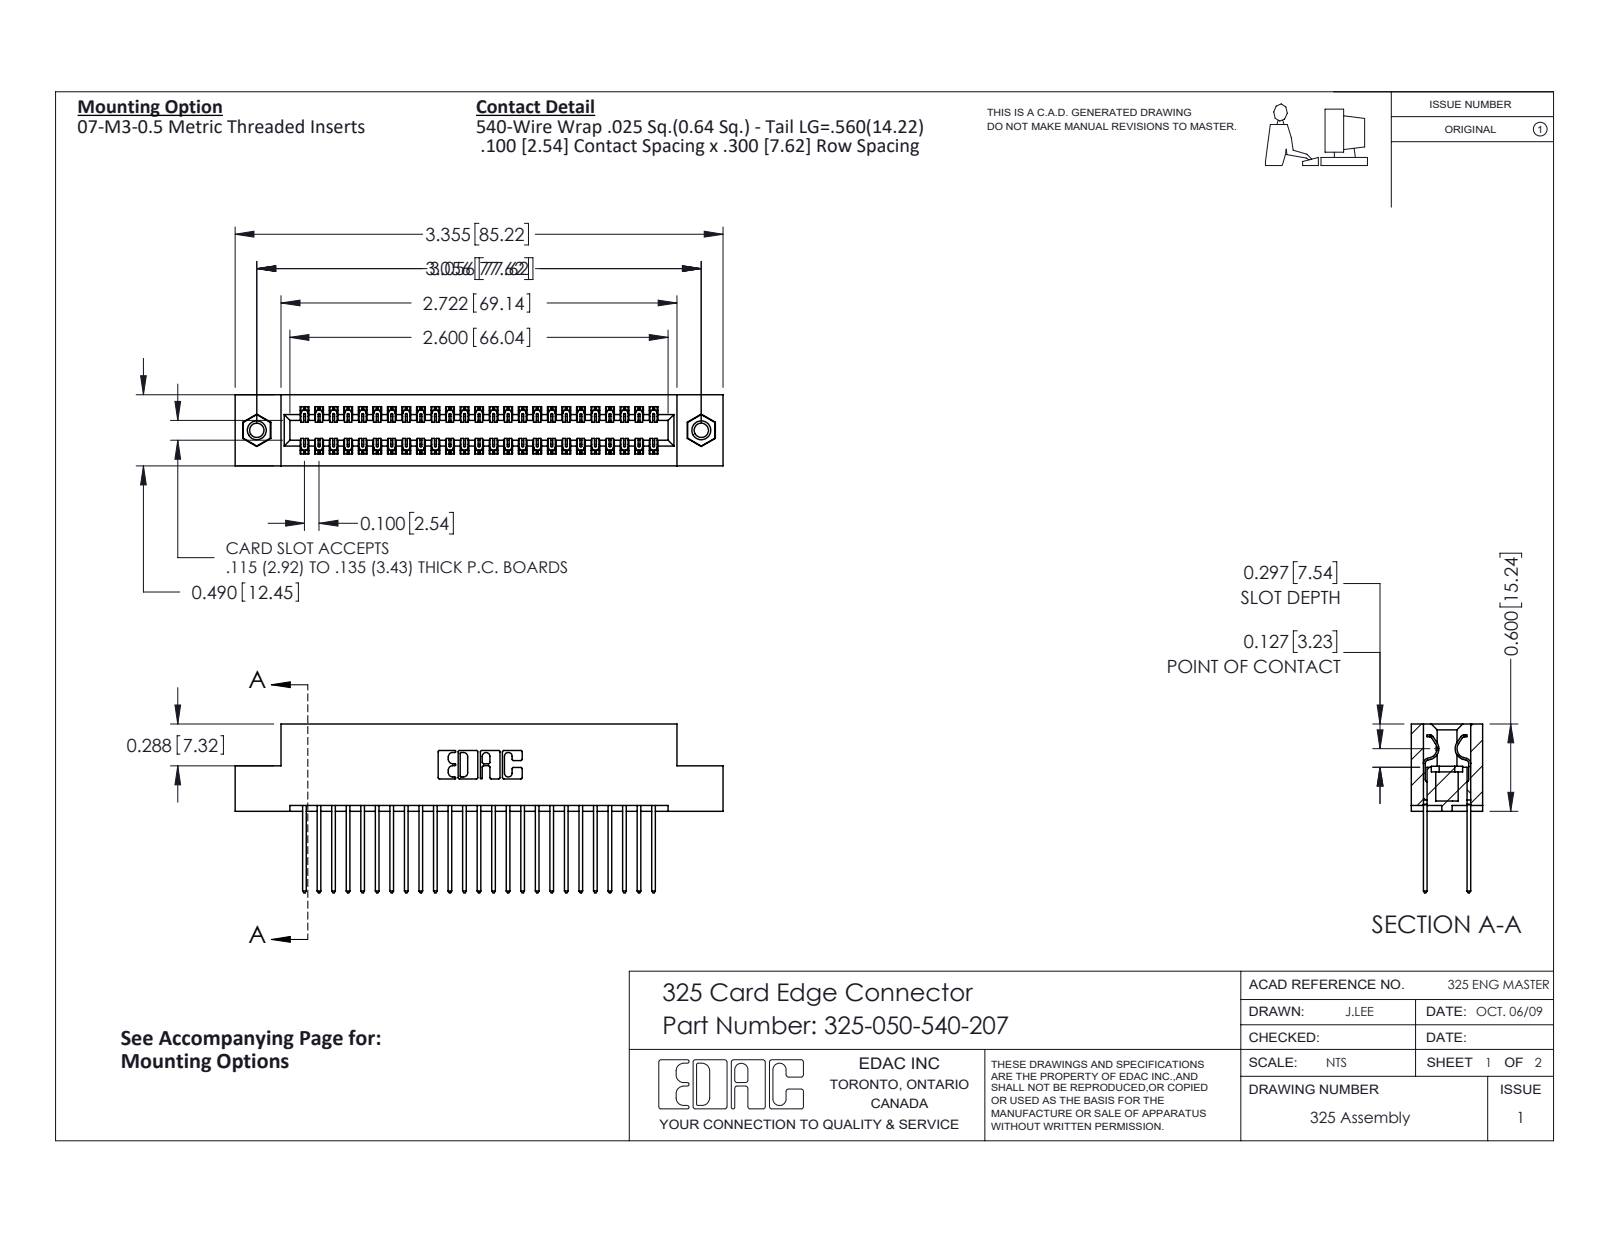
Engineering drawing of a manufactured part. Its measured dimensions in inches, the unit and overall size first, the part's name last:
Units: inches
Overall size (bounding box): 3.355 × 1.16 × 0.49
Round holes (diameter × count): ⌀0.098 ×2, ⌀0.125 ×2, ⌀0.16 ×2
Round bosses / shafts (diameter × count): ⌀0.155 ×2
Partial cylindrical surfaces — rounded edges, fillets, slot ends (radius × count): R0.006 ×75, R0.01 ×50, R0.01 ×22, R0.007 ×6, R0.031 ×6, R0.026 ×3, R0.014 ×2, R0.022 ×2
Main face-to-face distances: 0.083, 0.407, 0.3, 0.107, 0.383, 0.025, 0.49, 0.325, 0.275, 0.04
Hole centre spacings: 3.056
Volume: 0.673 in³ · Surface area: 21.5 in²
Bodies: 53 solids, 2774 faces (1902 planar, 856 cylindrical, 16 other)
Part name (STEP PRODUCT): 345-250-001_345-250-005-103; 325-050-540-207; 325-292-001_325-293-140; 325 Part_TI
STEP written by: SolidWorks 2016 (CONFIG_CONTROL_DESIGN)
